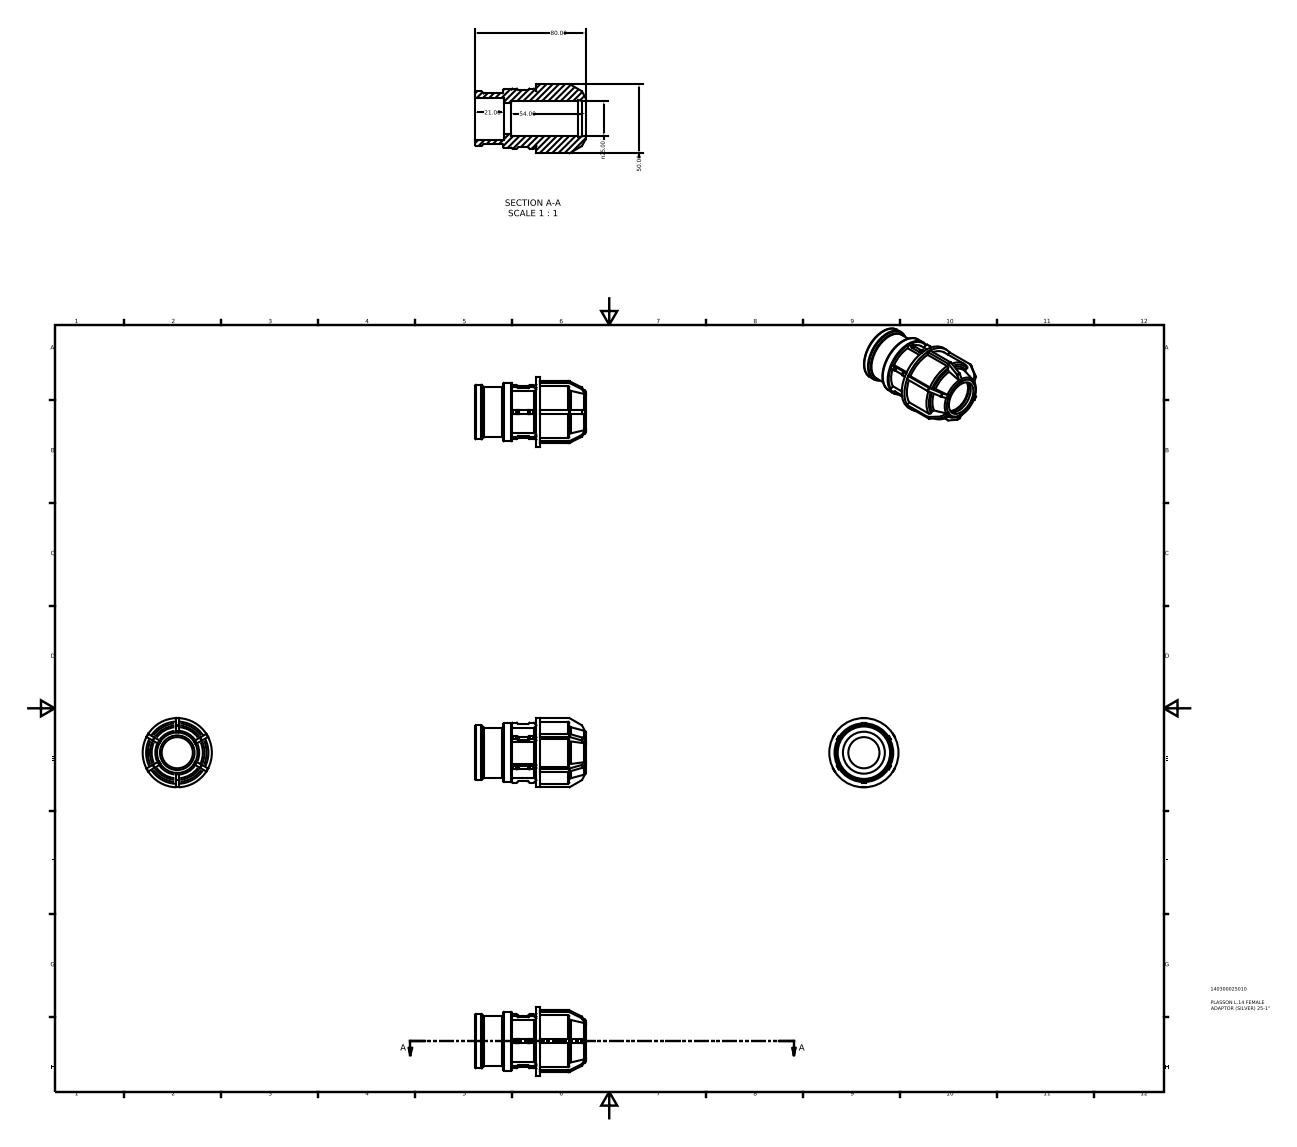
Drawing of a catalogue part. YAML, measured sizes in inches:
part_name: "140300025010"
step_written_by: "Autodesk Inventor 2015 (AUTOMOTIVE_DESIGN)"
units: inches
bodies: {solids: 1, faces: 261, planar: 159, cylindrical: 68, other: 34}
overall_size: [3.15, 1.969, 1.969]
volume: 3.534
surface_area: 33.89
round_holes:
  - {diameter: 0.886, count: 1}
  - {diameter: 0.984, count: 1}
  - {diameter: 1.193, count: 1}
round_bosses_or_shafts:
  - {diameter: 1.969, count: 1}
  - {diameter: 1.772, count: 1}
  - {diameter: 1.67, count: 1}
  - {diameter: 1.55, count: 1}
  - {diameter: 1.431, count: 1}
partial_cylinders:
  - {radius: 0.03, count: 48}
face_to_face_distances: [0.098, 1.746, 0.106, 0.222, 1.853, 0.827, 0.92, 1.026, 0.026, 1.049]
